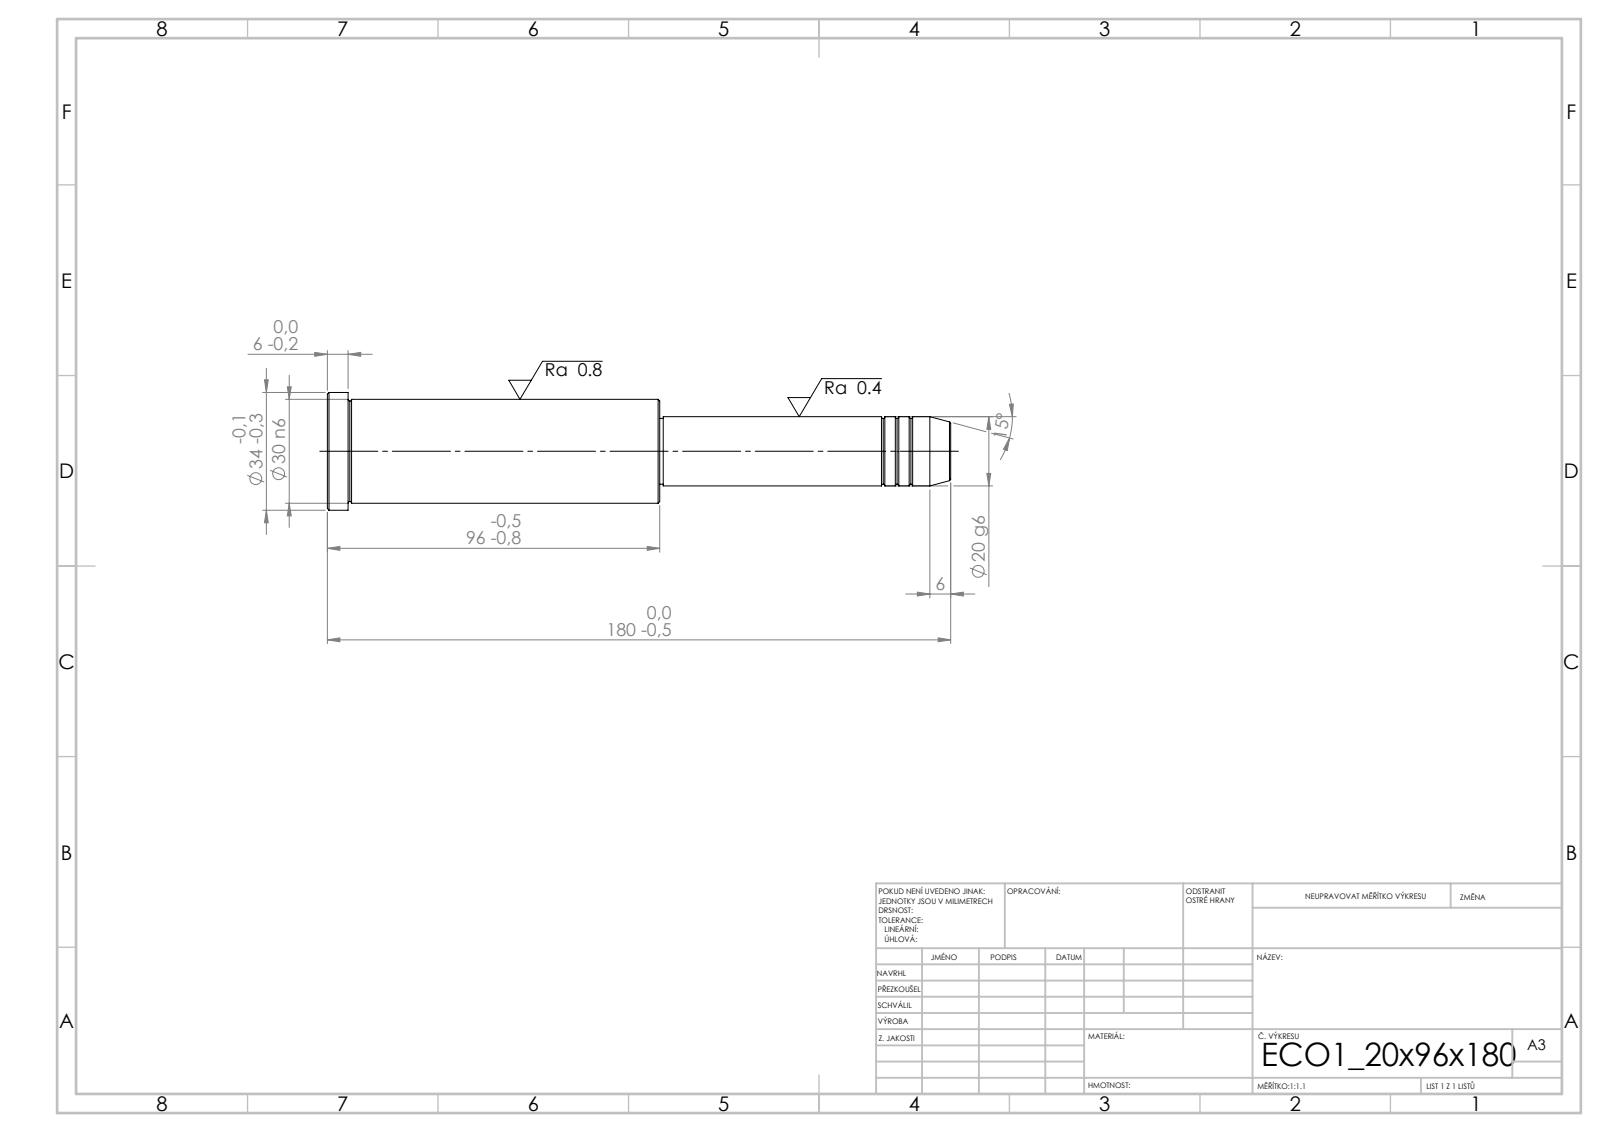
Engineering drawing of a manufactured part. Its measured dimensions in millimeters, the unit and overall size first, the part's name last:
Units: millimetres
Overall size (bounding box): 180 × 34 × 34
Round bosses / shafts (diameter × count): ⌀34 ×1, ⌀30 ×1, ⌀20 ×1, ⌀19 ×1
Main face-to-face distances: 96, 84, 180, 174, 90, 6, 83, 1, 91, 97
Volume: 95 001 mm³ · Surface area: 16 247 mm²
Bodies: 1 solid, 43 faces (5 planar, 14 cylindrical, 24 other)
STEP written by: SolidWorks 2019 (CONFIG_CONTROL_DESIGN)
